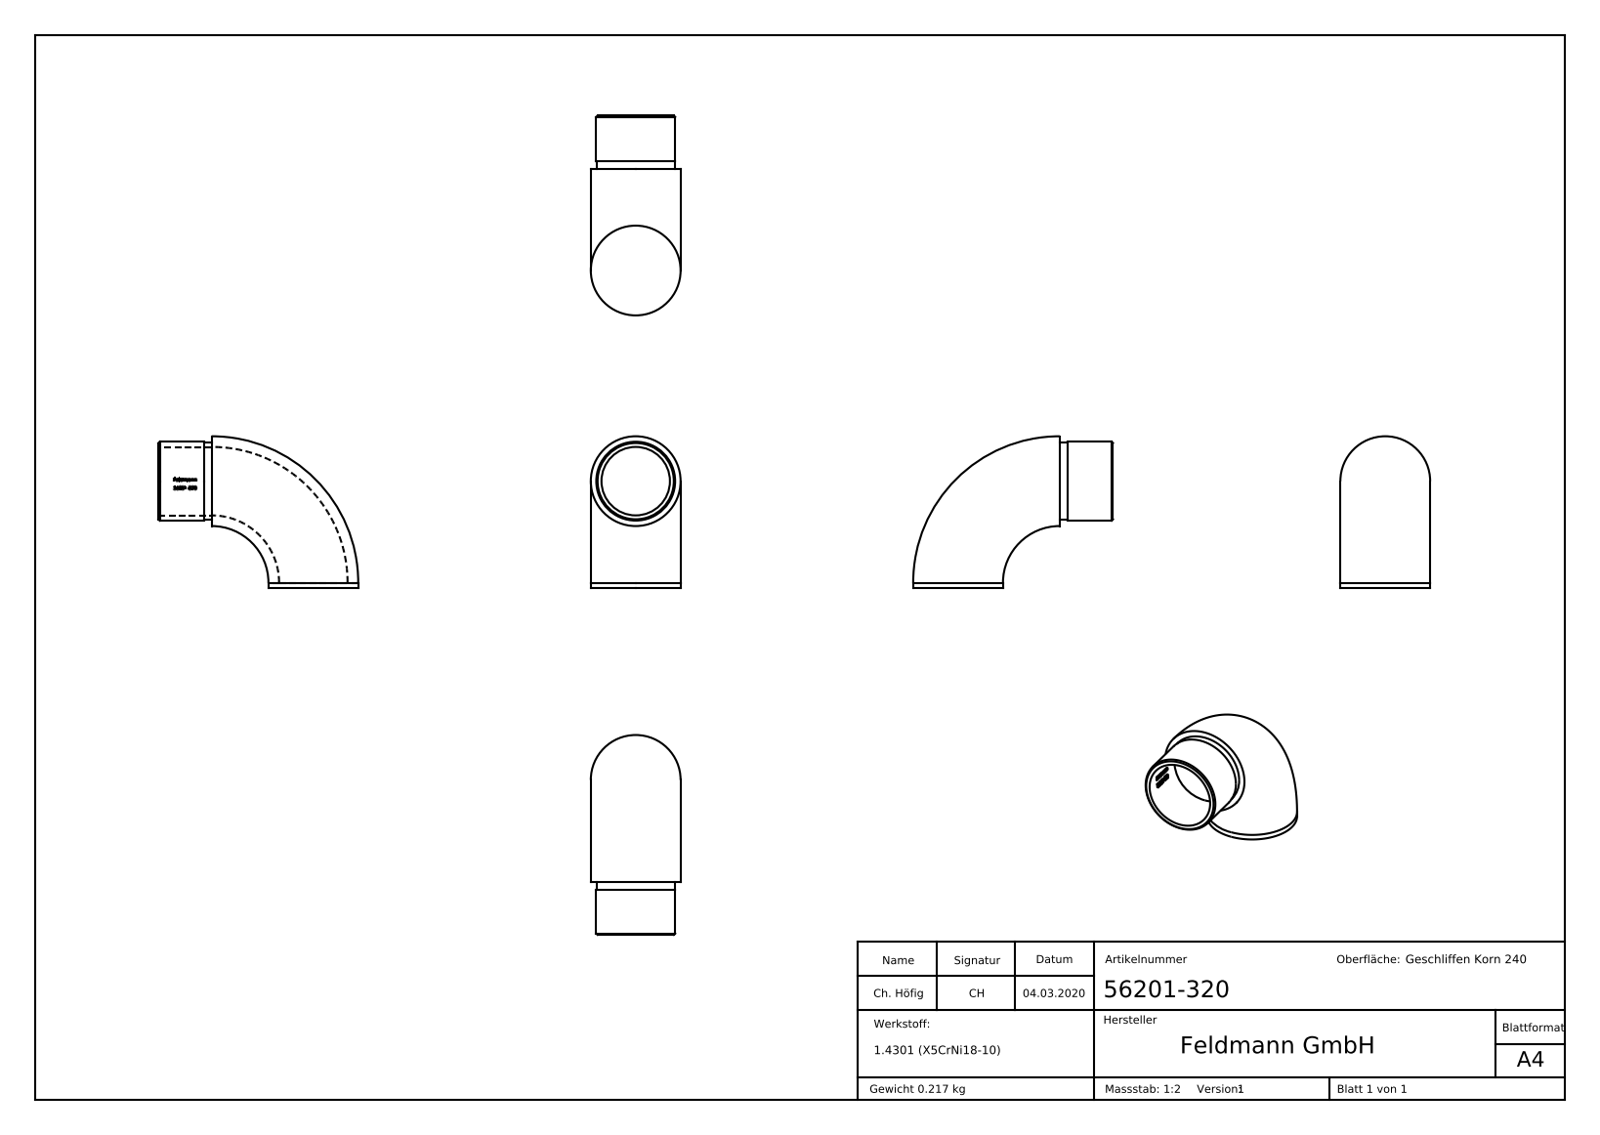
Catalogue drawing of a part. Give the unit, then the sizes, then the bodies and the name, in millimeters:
Units: millimetres
Overall size (bounding box): 75 × 57 × 33.7
Round holes (diameter × count): ⌀25.7 ×1
Round bosses / shafts (diameter × count): ⌀33.7 ×1, ⌀29.6 ×1, ⌀29.2 ×1
Partial cylindrical surfaces — rounded edges, fillets, slot ends (radius × count): R12.95 ×1
Main face-to-face distances: 2, 20, 3, 17, 2.97, 3.2, 0.39, 4.43, 1.32, 3.66
Volume: 27 470 mm³ · Surface area: 16 668 mm²
Bodies: 1 solid, 232 faces (93 planar, 27 cylindrical, 112 other)
Part name (STEP PRODUCT): 56201-320
STEP written by: SolidWorks 2015 (CONFIG_CONTROL_DESIGN)
